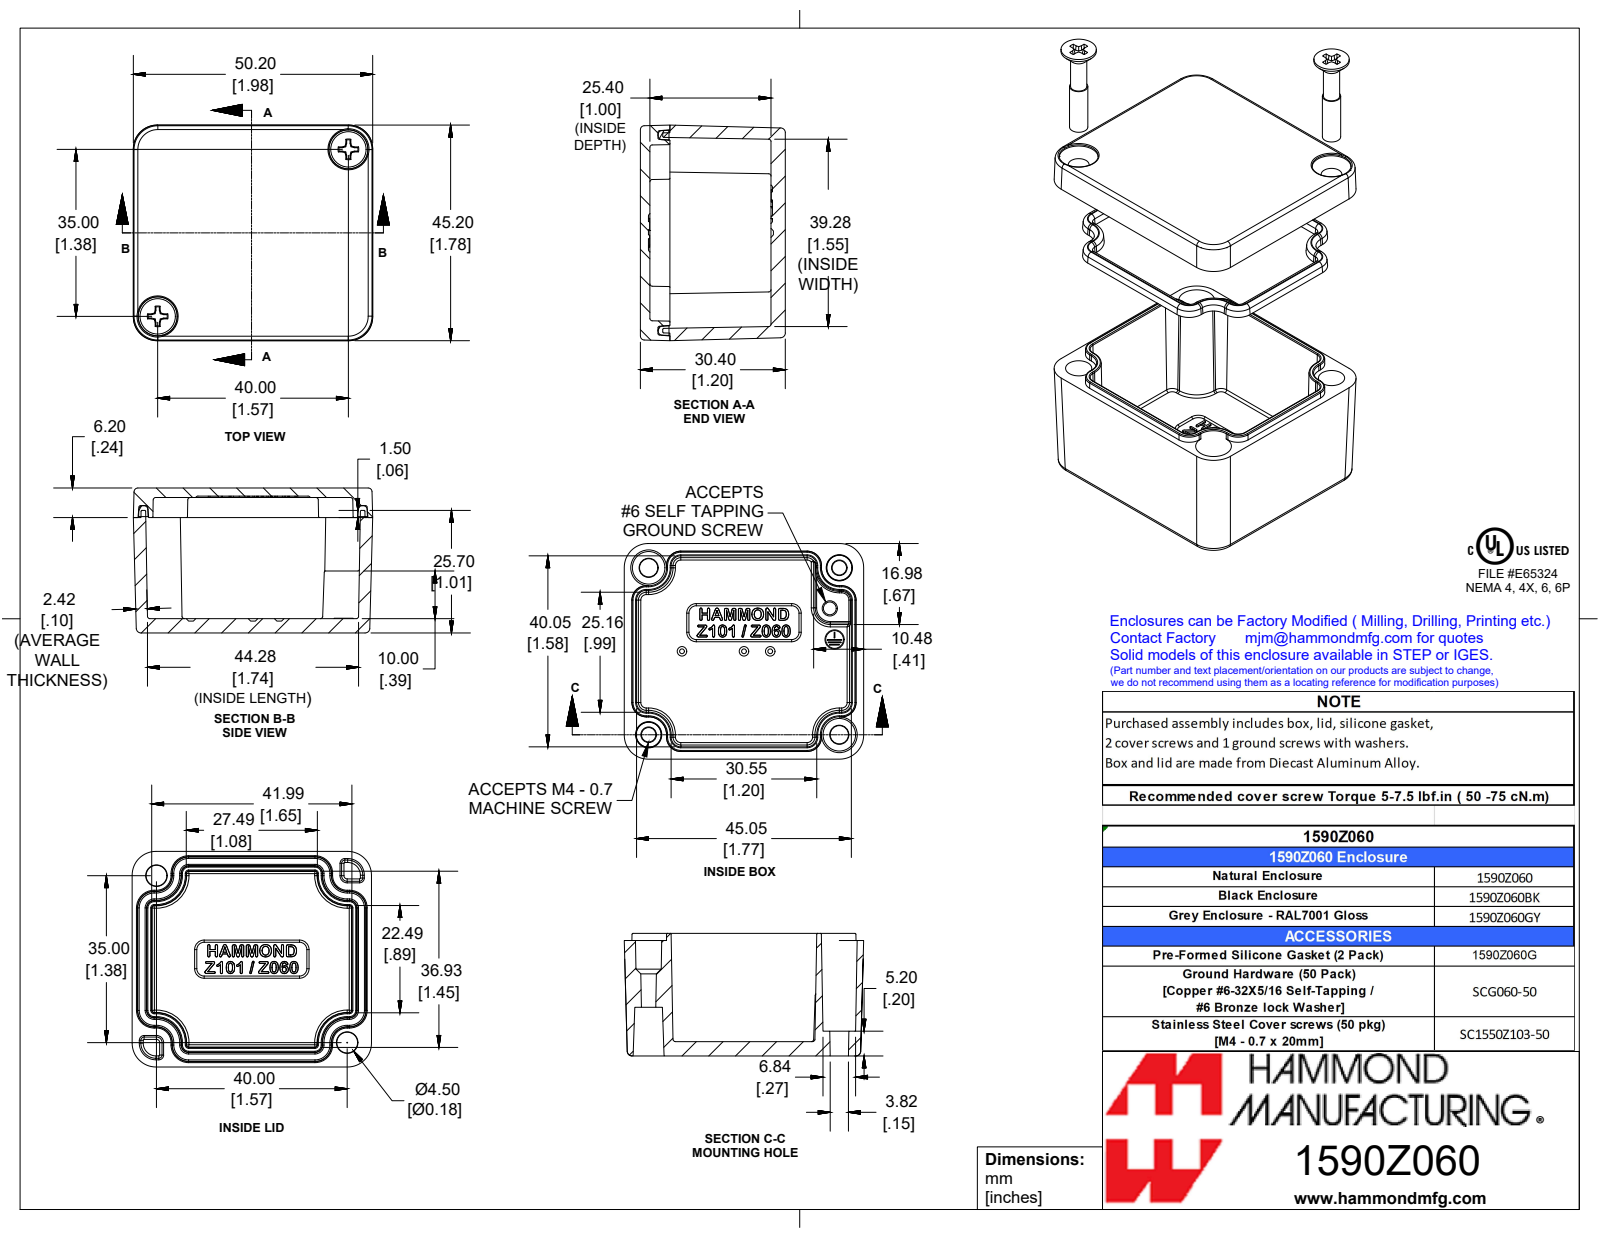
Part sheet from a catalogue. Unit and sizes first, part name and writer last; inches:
Units: inches
Overall size (bounding box): 1.976 × 1.78 × 1.197
Round bosses / shafts (diameter × count): ⌀0.15 ×2, ⌀0.135 ×2
Partial cylindrical surfaces — rounded edges, fillets, slot ends (radius × count): R0.008 ×40, R0.02 ×34, R0.012 ×22, R0.197 ×8, R0.031 ×4, R0.039 ×4
Main face-to-face distances: 1.197, 0.118, 0.079, 1.079, 1.118, 1, 0.165, 0.953, 0.835, 0.244
Volume: 1.515 in³ · Surface area: 33.7 in²
Bodies: 4 solids, 1051 faces (333 planar, 158 cylindrical, 560 other)
Part name (STEP PRODUCT): 1590Z060BK
STEP written by: SolidWorks 2019 (CONFIG_CONTROL_DESIGN)
